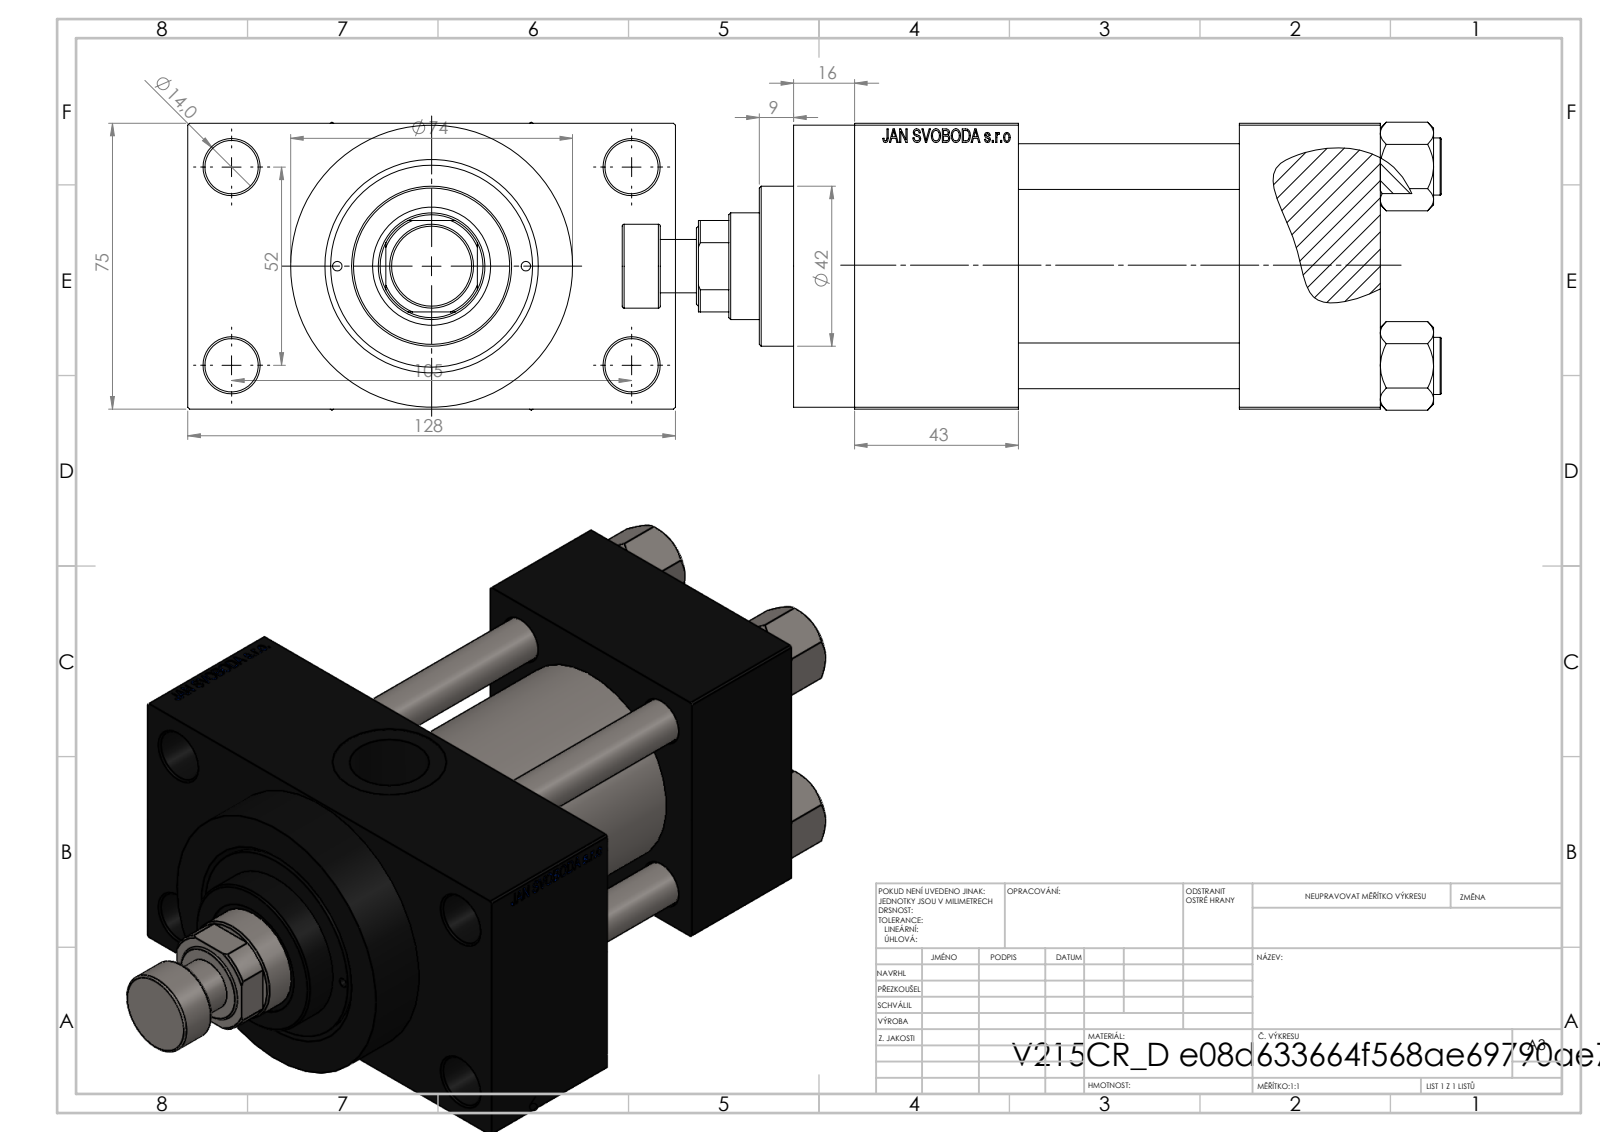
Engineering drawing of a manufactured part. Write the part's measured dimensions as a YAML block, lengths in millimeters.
part_name: "V215CR_VCP_D; V215_VC_A; V215CR_D_Body; NUT_M5_D (+2 more)"
step_written_by: "SolidWorks 2019 (CONFIG_CONTROL_DESIGN)"
units: millimeters
bodies: {solids: 12, faces: 1126, planar: 503, cylindrical: 97, other: 526}
overall_size: [215, 128, 75.54]
volume: 820443
surface_area: 171037
round_holes:
  - {diameter: 12, count: 4}
  - {diameter: 14, count: 4}
  - {diameter: 2.5, count: 2}
  - {diameter: 7, count: 2}
  - {diameter: 20.96, count: 2}
  - {diameter: 30, count: 2}
  - {diameter: 18.5, count: 1}
  - {diameter: 28, count: 1}
  - {diameter: 31, count: 1}
  - {diameter: 41, count: 1}
  - {diameter: 50, count: 1}
  - {diameter: 53, count: 1}
round_bosses_or_shafts:
  - {diameter: 15, count: 4}
  - {diameter: 74, count: 1}
  - {diameter: 56, count: 1}
  - {diameter: 42, count: 1}
  - {diameter: 22, count: 1}
  - {diameter: 14, count: 1}
partial_cylinders:
  - {radius: 13.5, count: 1}
face_to_face_distances: [75, 58, 37, 95, 26.5, 101.5, 138, 101, 43, 16]
hole_center_spacings: [26.19, 26.35, 36.98, 38.03, 52.3, 57.22, 58.43, 58.59]
